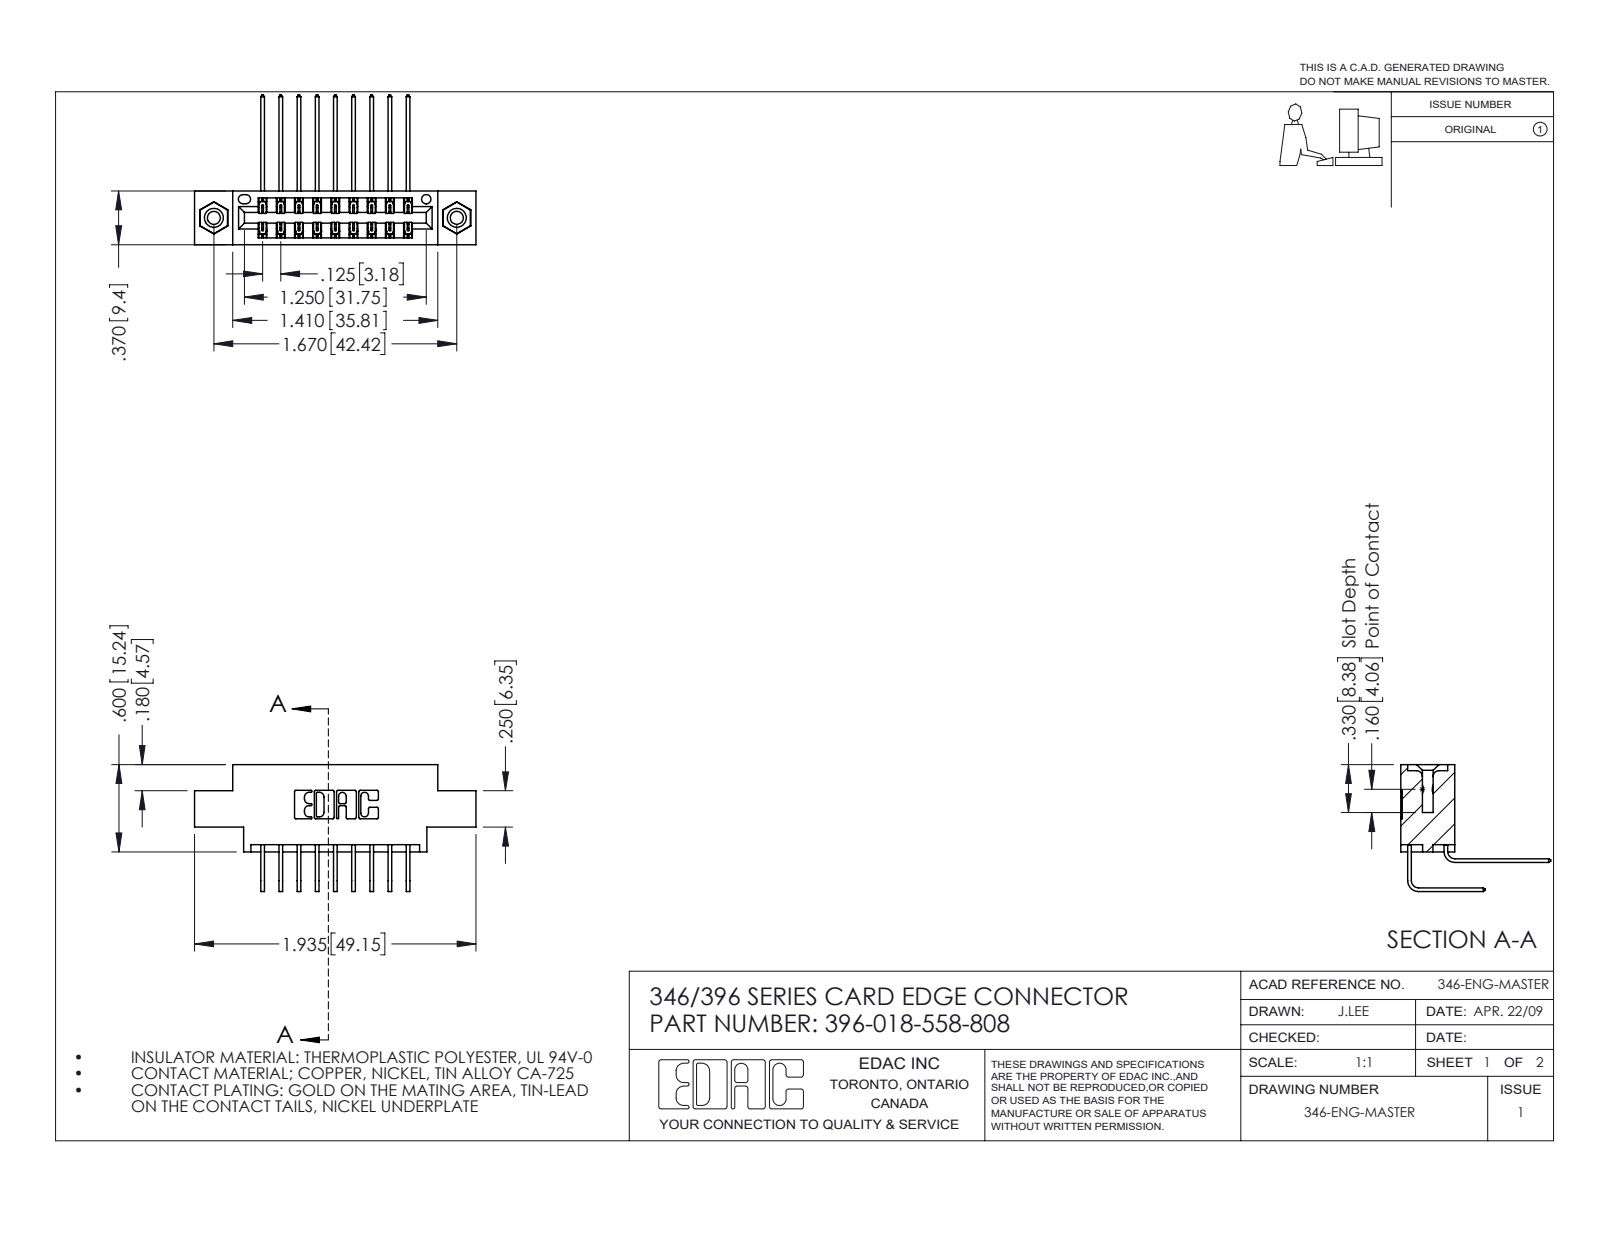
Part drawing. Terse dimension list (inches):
name: 345-292-001_558 559 Tail - 1; 345-250-001_345-250-003-102; 396-018-558-808; 346 Part_0.170 Offset - 0.156 Dia-TI (+1 more)
written by: SolidWorks 2016 (CONFIG_CONTROL_DESIGN)
unit: in
bodies: 21 solids, 1158 faces (778 planar, 364 cylindrical, 16 other)
size: 1.935 × 1.03 × 0.873
volume: 0.273 in³; area: 9.821 in²
holes: 2× ⌀0.089, 2× ⌀0.125, 2× ⌀0.156, 1× ⌀0.064
bosses: 2× ⌀0.155
rounds: 27× R0.006, 22× R0.01, 6× R0.007, 6× R0.031, 3× R0.026, 2× R0.014, 2× R0.022, 2× R0.024
face distances: 0.25, 0.048, 0.322, 0.37, 0.025, 0.072, 0.298, 0.222, 0.148, 0.275
hole spacings: 0.246, 1.465, 1.67
